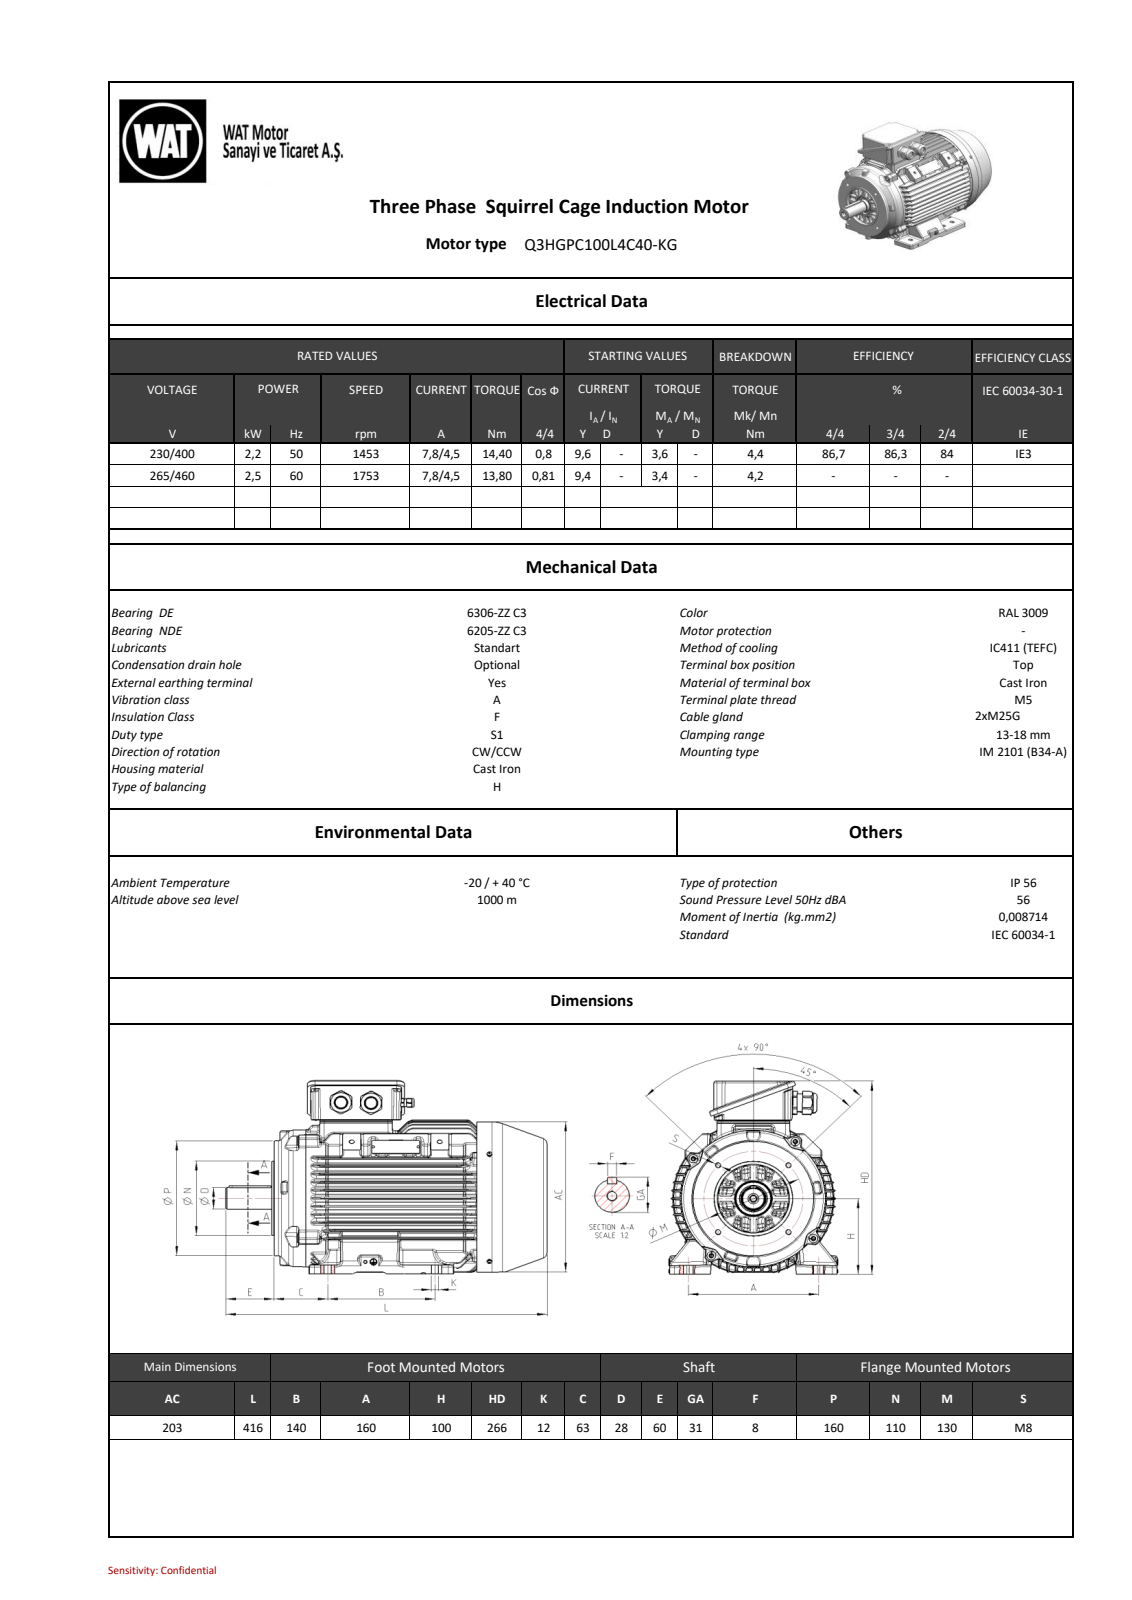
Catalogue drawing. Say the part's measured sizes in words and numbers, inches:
The part is named "26000A30F4D8row0". Its 3-D file was written by "SIEMENS PLM Software NX 11.0 (AUTOMOTIVE_DESIGN)". It is 0 solids with 4747 faces: 924 planar, 1279 cylindrical and 2544 other. Overall it measures 16.378 by 10.452 by 8.043 inches. Round holes: 8 of diameter 0.197, 6 of diameter 0.268, 3 of diameter 0.394, 2 of diameter 0.677, 1 of diameter 0.165, 1 of diameter 0.256, 1 of diameter 0.335, 1 of diameter 0.413, 1 of diameter 1.709, 1 of diameter 1.717, 1 of diameter 7.756. Round bosses or shafts: 8 of diameter 0.394, 4 of diameter 0.472, 4 of diameter 0.341, 4 of diameter 0.315, 4 of diameter 0.157, 2 of diameter 1.091, 2 of diameter 0.994, 2 of diameter 0.787. Partial cylindrical surfaces (rounded edges, fillets, slot ends): 378 of radius 0.118, 125 of radius 0.059, 50 of radius 0.079, 42 of radius 0.071, 38 of radius 0.039, 31 of radius 0.01, 12 of radius 1.043, 12 of radius 1.358. The main face-to-face distances are 0.532, 0.536, 1.068, 3.099, 2.031, 2.563, 1.607, 1.075, 0.539, 1.492. The hole center spacings are 1.097, 3.524, 3.979, 4.7, 6.06, 4.983, 2.559, 3.619.
